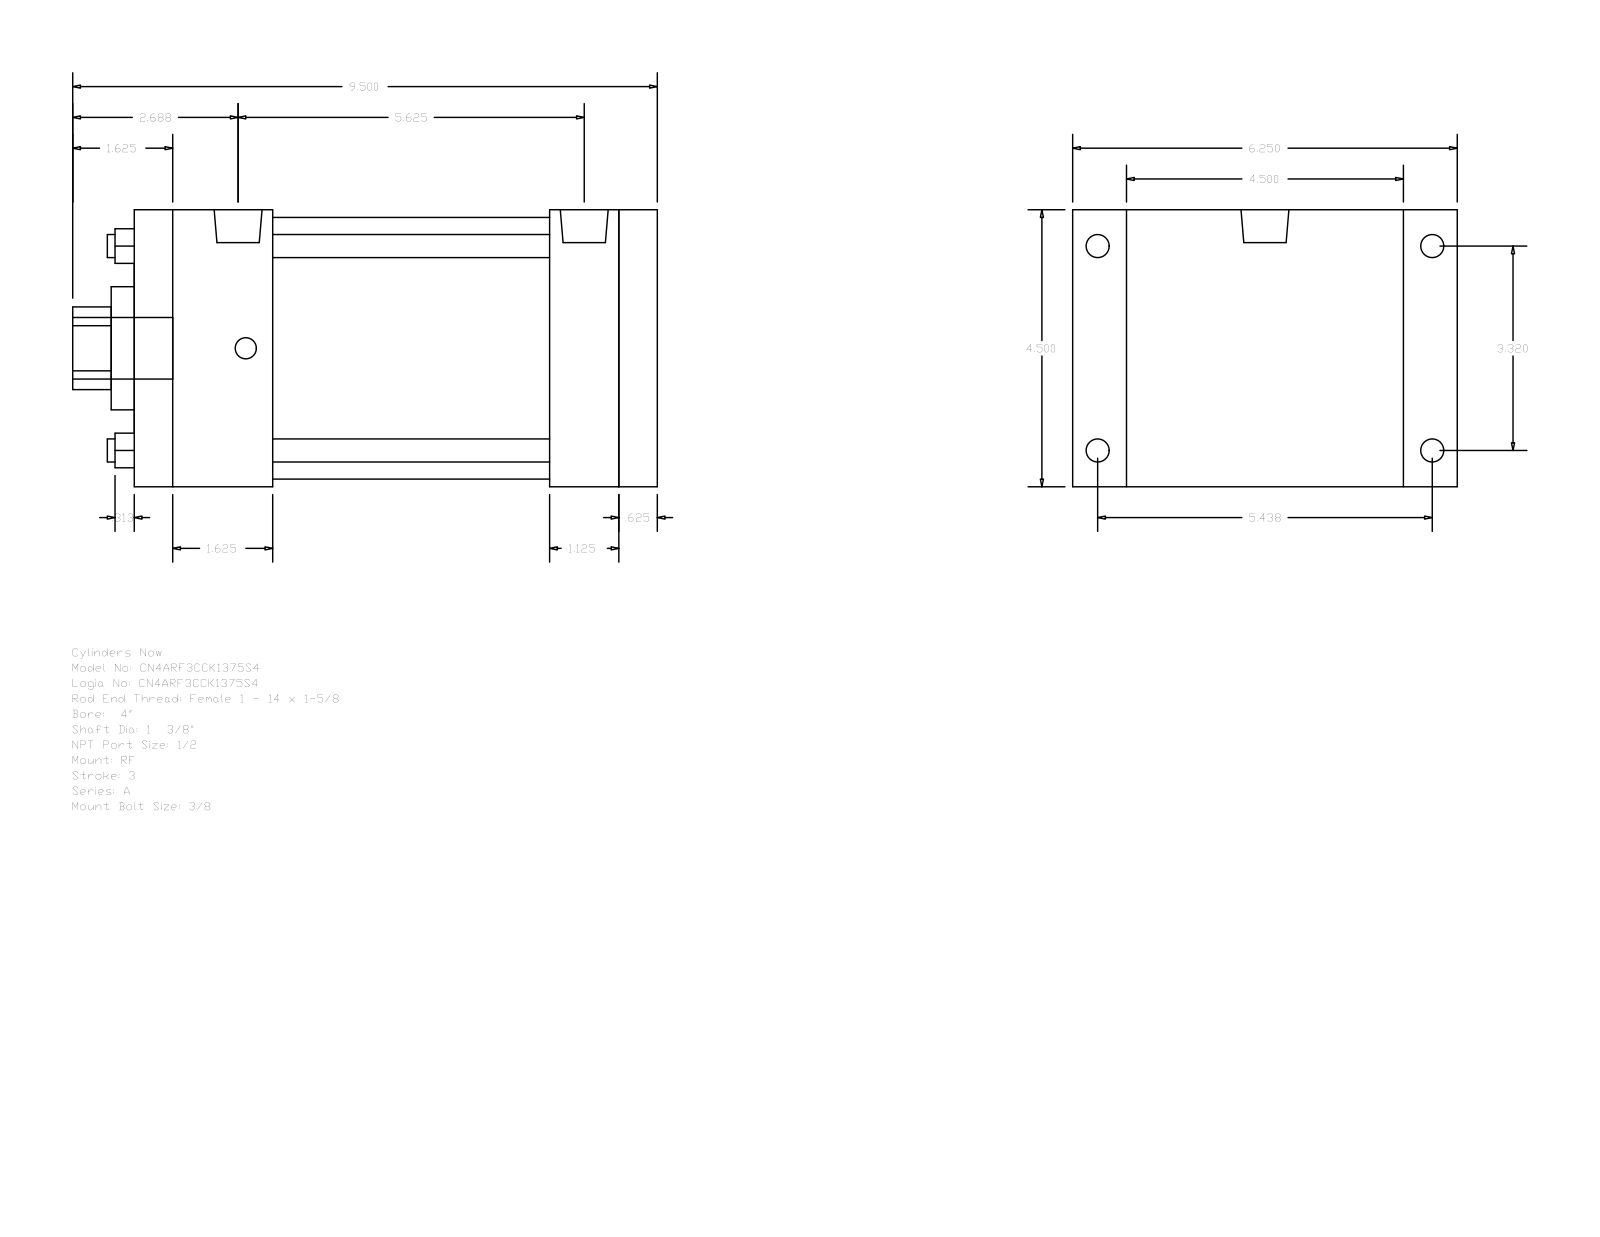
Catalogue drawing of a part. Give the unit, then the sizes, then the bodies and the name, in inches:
Units: inches
Overall size (bounding box): 9.5 × 6.25 × 4.5
Round holes (diameter × count): ⌀0.375 ×4, ⌀1.375 ×1, ⌀2 ×1, ⌀4.25 ×1
Round bosses / shafts (diameter × count): ⌀0.375 ×4, ⌀0.344 ×4, ⌀0.778 ×2, ⌀1 ×1
Partial cylindrical surfaces — rounded edges, fillets, slot ends (radius × count): R0.672 ×1
Main face-to-face distances: 4.5, 8.5, 0.625, 7.875, 1.125, 0.875, 5.375, 6.75, 1.75, 2.25
Hole centre spacings: 2.347, 3.32, 4.695
Bodies: 0 solids, 92 faces (64 planar, 28 cylindrical, 0 other)
Part name (STEP PRODUCT): A_RF__0400_1.375
STEP written by: GSSL Pune (CONFIG_CONTROL_DESIGN)
